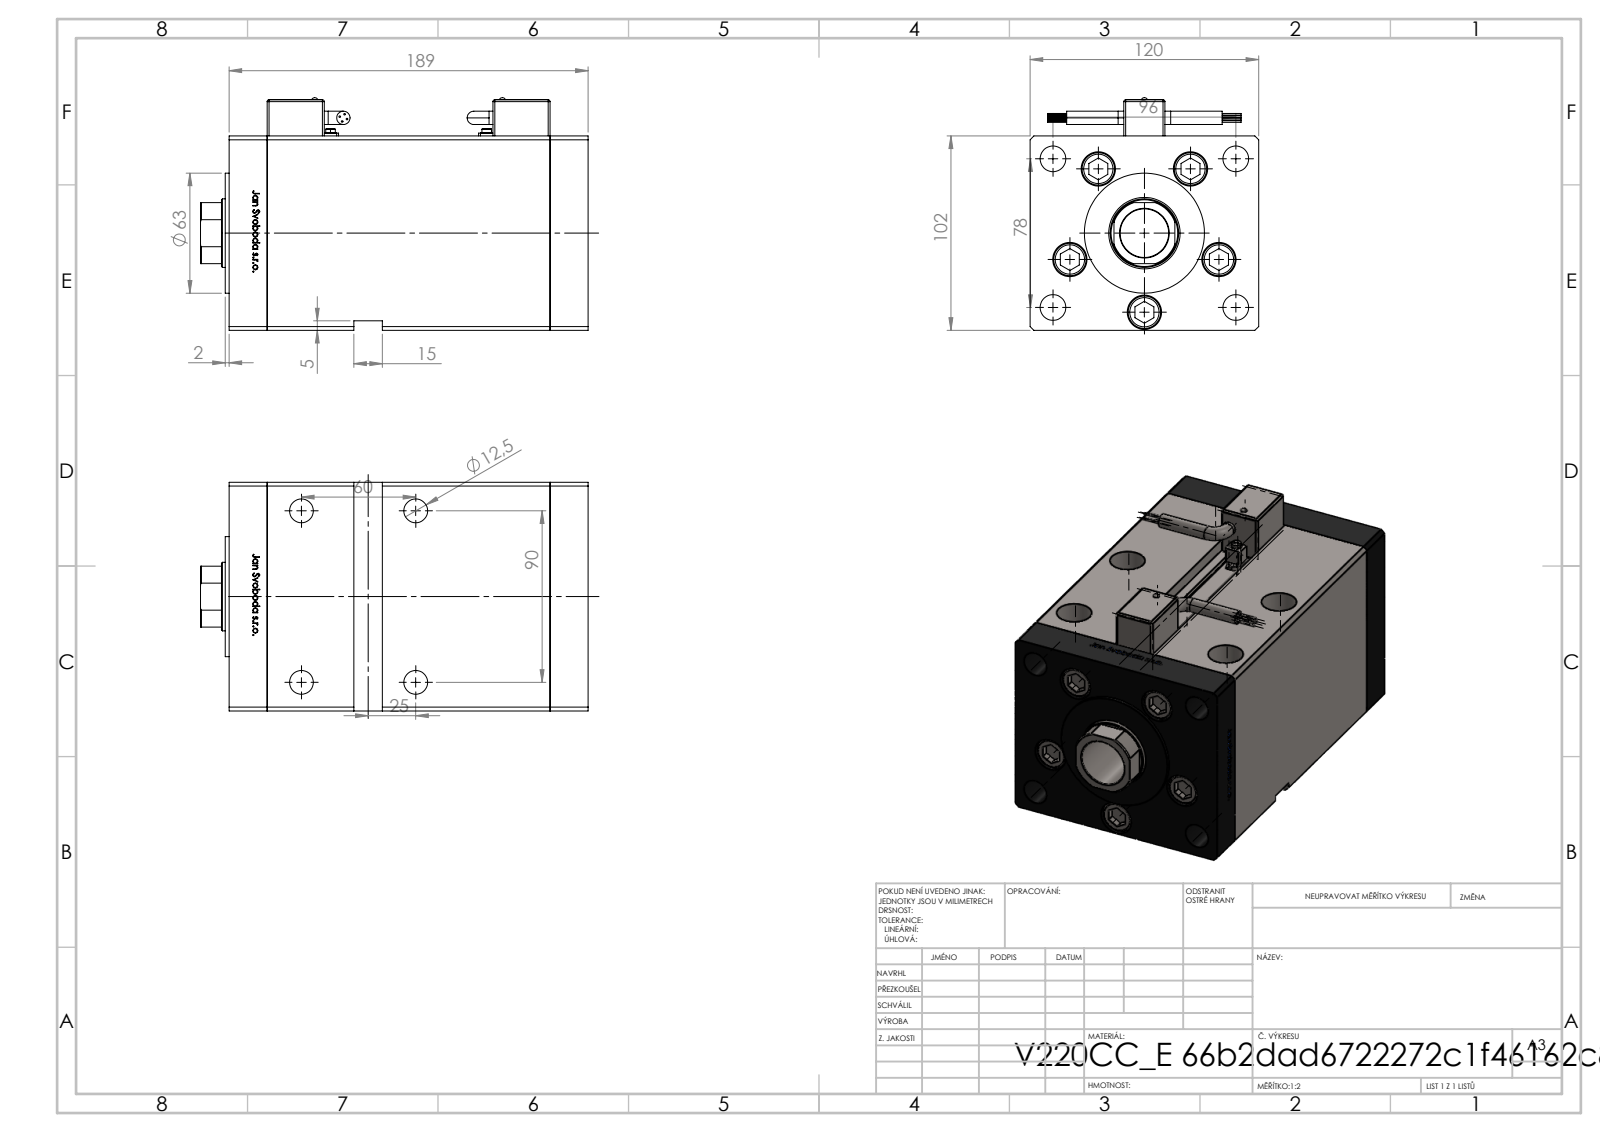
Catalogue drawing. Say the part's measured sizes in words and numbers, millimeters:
The part is named "V220C_FRONT_E; Magnetic_Switch_MSU4; V220C BACK_E; ALLEN BOLT (+2 more)". Its 3-D file was written by "SolidWorks 2019 (CONFIG_CONTROL_DESIGN)". It is 16 solids with 1418 faces: 553 planar, 255 cylindrical and 610 other. Overall it measures 203.5 by 122.1 by 120 millimeters. Its volume is 2 010 000 cubic millimeters and its surface area 285 085 square millimeters. Round holes: 9 of diameter 13.5, 5 of diameter 18, 4 of diameter 12.5, 4 of diameter 18.5, 2 of diameter 2, 2 of diameter 3.6, 2 of diameter 5, 2 of diameter 7, 2 of diameter 13.16, 1 of diameter 25.5, 1 of diameter 36, 1 of diameter 37.5. Round bosses or shafts: 8 of diameter 0.85, 5 of diameter 17, 5 of diameter 8, 4 of diameter 7, 2 of diameter 6, 2 of diameter 3.5, 2 of diameter 2.5, 1 of diameter 63. Partial cylindrical surfaces (rounded edges, fillets, slot ends): 24 of radius 1, 4 of radius 4, 2 of radius 0.93, 1 of radius 17.5. The main face-to-face distances are 120, 20, 148.5, 168.5, 102, 34.25, 188.5, 14.25, 134.25, 154.25. The hole center spacings are 41.5, 61.85, 8.25, 24.39, 26.69, 45.54, 47.51, 47.92.
